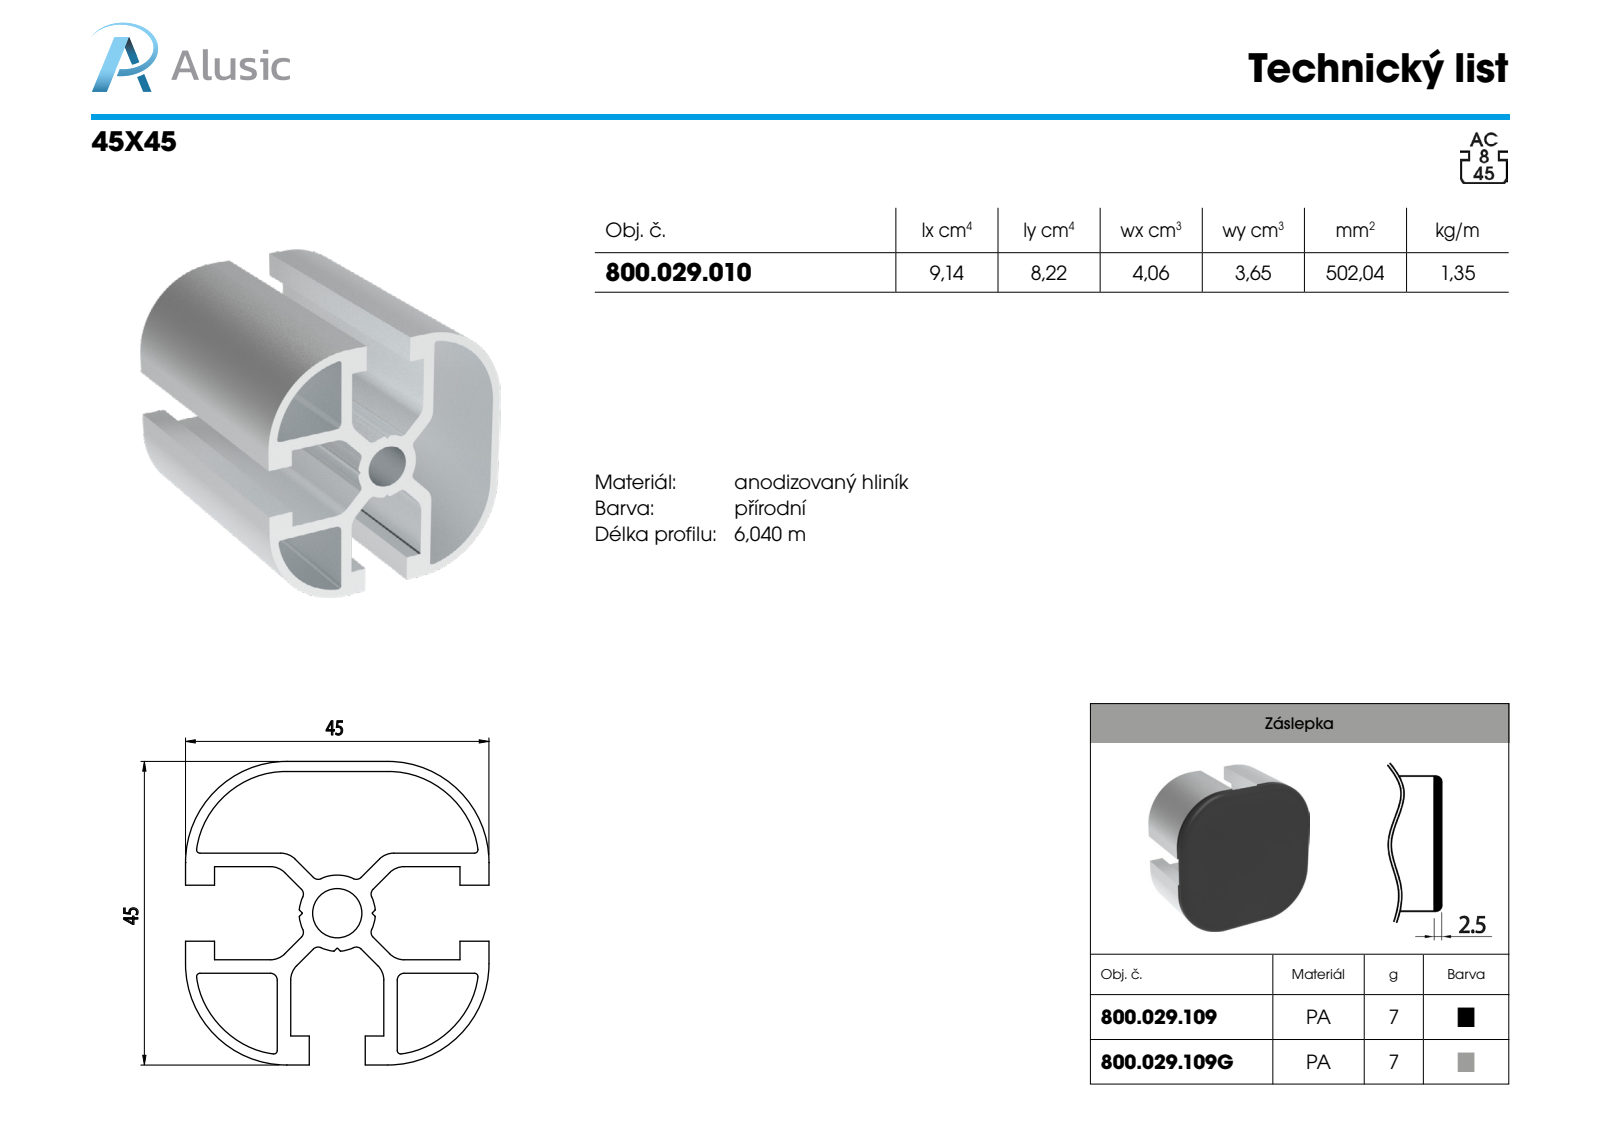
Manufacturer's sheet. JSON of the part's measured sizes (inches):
{"part_name": "800.029.010", "step_written_by": "SolidWorks 2018 (AUTOMOTIVE_DESIGN)", "units": "inches", "bodies": {"solids": 1, "faces": 102, "planar": 48, "cylindrical": 54, "other": 0}, "overall_size": [3.937, 1.772, 1.772], "volume_in3": 3.064, "surface_area_in2": 76.68, "round_holes": [[0.287, 1]], "partial_cylinders_radius": [[0.039, 10], [0.004, 9], [0.118, 8], [0.02, 6], [0.531, 4], [0.591, 4], [0.222, 1]], "face_to_face_distances": [0.079, 0.622, 0.535, 0.614, 1.157, 1.236, 0.701, 0.514, 0.435, 0.187]}
